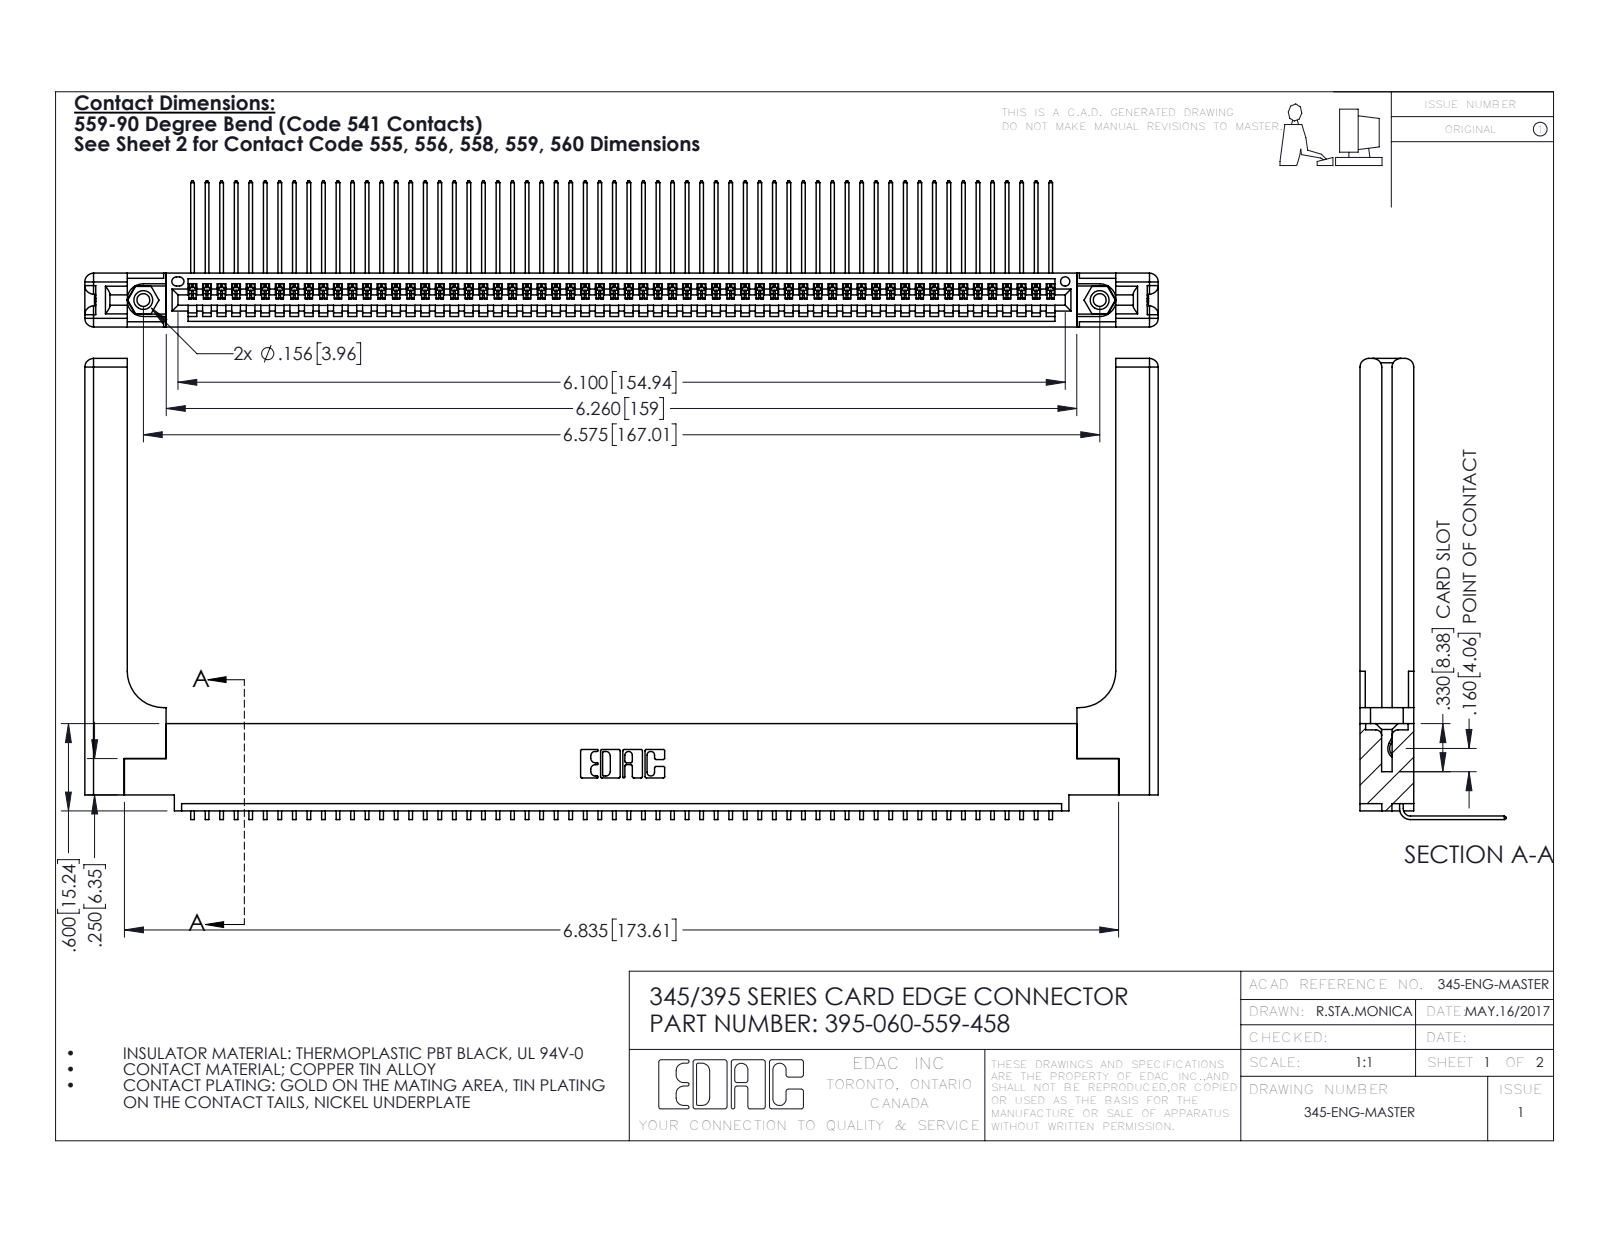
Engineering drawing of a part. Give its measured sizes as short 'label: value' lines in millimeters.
name: 345 Part_0.110 Offset - 0.156 Dia-TH; 345-292-001_558 559 Tail - 1; 395-060-559-458; 345-220-058_345-220-058 (+1 more)
written by: SolidWorks 2016 (CONFIG_CONTROL_DESIGN)
unit: mm
bodies: 65 solids, 3986 faces (2752 planar, 1174 cylindrical, 60 other)
size: 187.4 × 80.5 × 25.5
volume: 26 580 mm³; area: 30 830 mm²
holes: 2× ⌀2.3, 2× ⌀3.2, 2× ⌀4, 1× ⌀1.6
bosses: 2× ⌀3.9
rounds: 120× R0.2, 22× R0.3, 16× R1.5, 6× R0.2, 6× R0.8, 3× R0.7, 2× R0.8, 2× R0.8
face distances: 1.8, 9.4, 7.6, 2.5, 6.9, 0.6, 5.1, 5.7, 3.8, 3.8
hole spacings: 6.9, 161, 167
